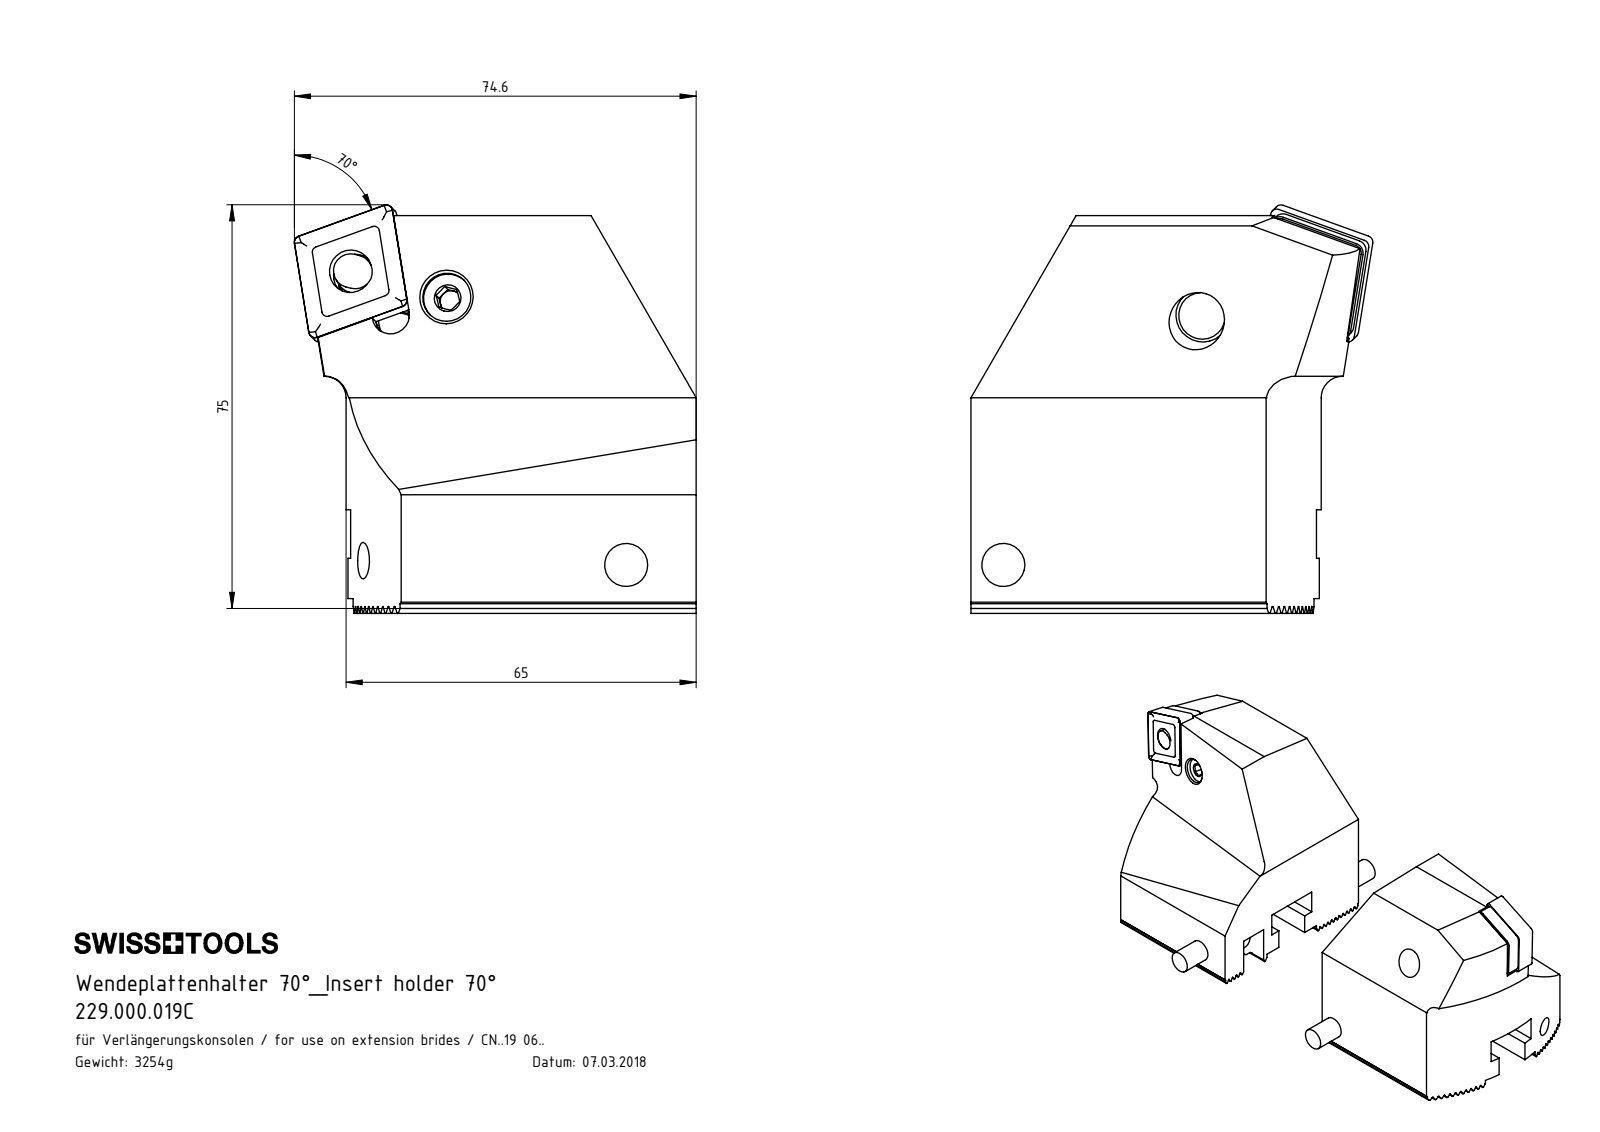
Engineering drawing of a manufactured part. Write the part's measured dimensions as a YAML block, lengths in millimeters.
part_name: "WCF-ER1.101.000; WCF; WCF-ER3.101.000_A; WCF-ER4.101.027_A (+6 more)"
step_written_by: "SolidWorks 2017 (CONFIG_CONTROL_DESIGN)"
units: millimeters
bodies: {solids: 18, faces: 1312, planar: 784, cylindrical: 172, other: 356}
overall_size: [200.21, 94, 75.79]
volume: 411183
surface_area: 74323
round_holes:
  - {diameter: 8, count: 4}
  - {diameter: 6.8, count: 2}
  - {diameter: 7.94, count: 2}
  - {diameter: 9, count: 2}
  - {diameter: 9.6, count: 2}
  - {diameter: 10.2, count: 2}
round_bosses_or_shafts:
  - {diameter: 10, count: 2}
  - {diameter: 9.9, count: 2}
  - {diameter: 8.6, count: 2}
  - {diameter: 8, count: 2}
  - {diameter: 5.5, count: 2}
  - {diameter: 4.45, count: 2}
partial_cylinders:
  - {radius: 0.14, count: 22}
  - {radius: 1.2, count: 8}
  - {radius: 1.8, count: 8}
  - {radius: 4.15, count: 8}
  - {radius: 4.7, count: 3}
  - {radius: 3.1, count: 2}
  - {radius: 3.5, count: 2}
  - {radius: 3.65, count: 2}
face_to_face_distances: [1.73, 6.93, 8.66, 70, 3.46, 5.2, 41.57, 43.3, 24.5, 45.5]
hole_center_spacings: [7, 18.55, 70, 18.8, 18.81, 40, 63, 77]
